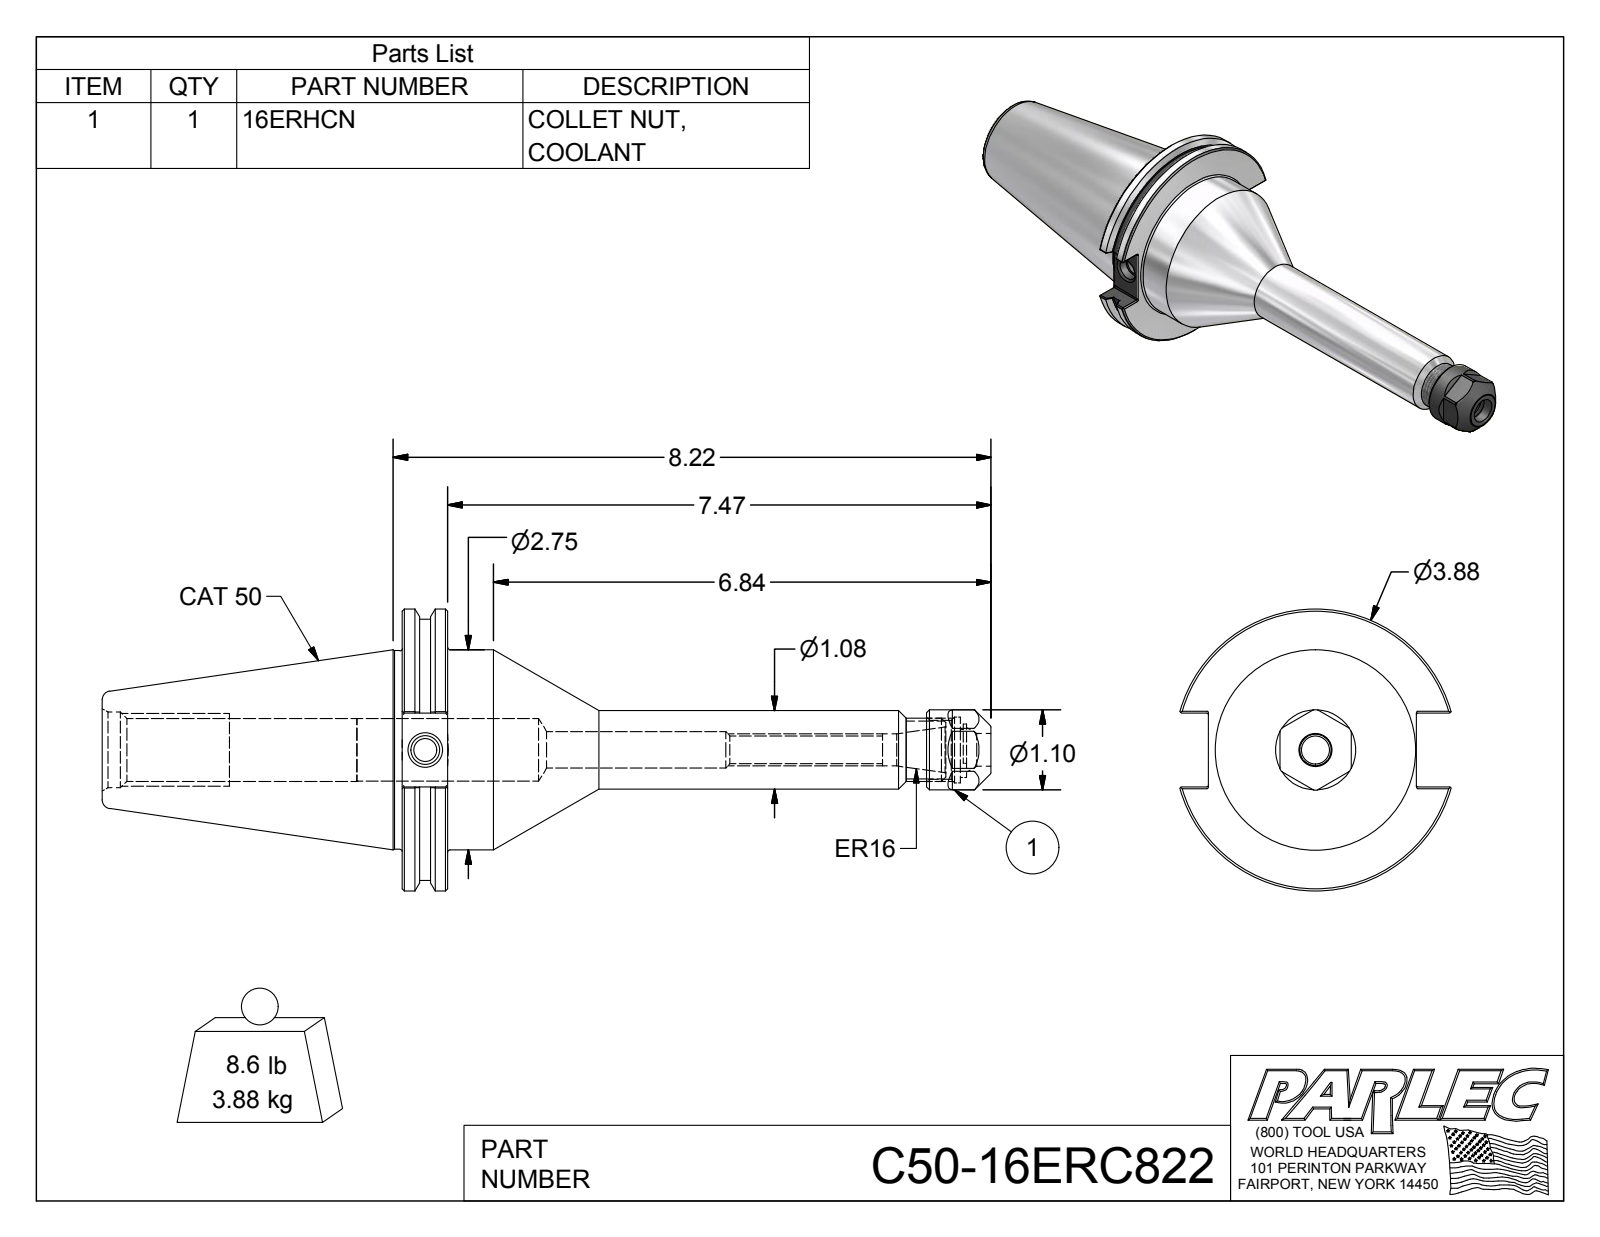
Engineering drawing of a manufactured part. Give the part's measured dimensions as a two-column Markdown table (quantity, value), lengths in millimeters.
| quantity | value |
| --- | --- |
| part name | C50-16ER8-1; 16ERHCN; C50-16ERC822 |
| STEP written by | Autodesk Inventor 2016 (AUTOMOTIVE_DESIGN) |
| units | millimeters |
| bodies | 2 solids, 132 faces (50 planar, 36 cylindrical, 46 other) |
| overall size | 310.39 × 98.42 × 94.71 |
| volume | 453 740 mm³ |
| surface area | 71 289 mm² |
| round holes (diameter × count) | 8 × 1, 9.73 × 1, 10.13 × 1, 11.18 × 1, 11.5 × 1, 12.7 × 1, 16.8 × 1, 20.5 × 1, 21.95 × 1, 21.97 × 1, 23 × 1, 26.37 × 1 |
| round bosses / shafts (diameter × count) | 98.42 × 1, 91.29 × 1, 69.85 × 1, 69.34 × 1, 28 × 1, 27.43 × 1, 22 × 1 |
| partial cylindrical surfaces (radius × count) | 0.51 × 12, 9 × 1 |
| main face-to-face distances | 31.88, 15.88, 16, 24.86, 104.77, 120.65, 136.65, 72.65, 25.78, 22 |
| hole center spacings | 1.3 |
